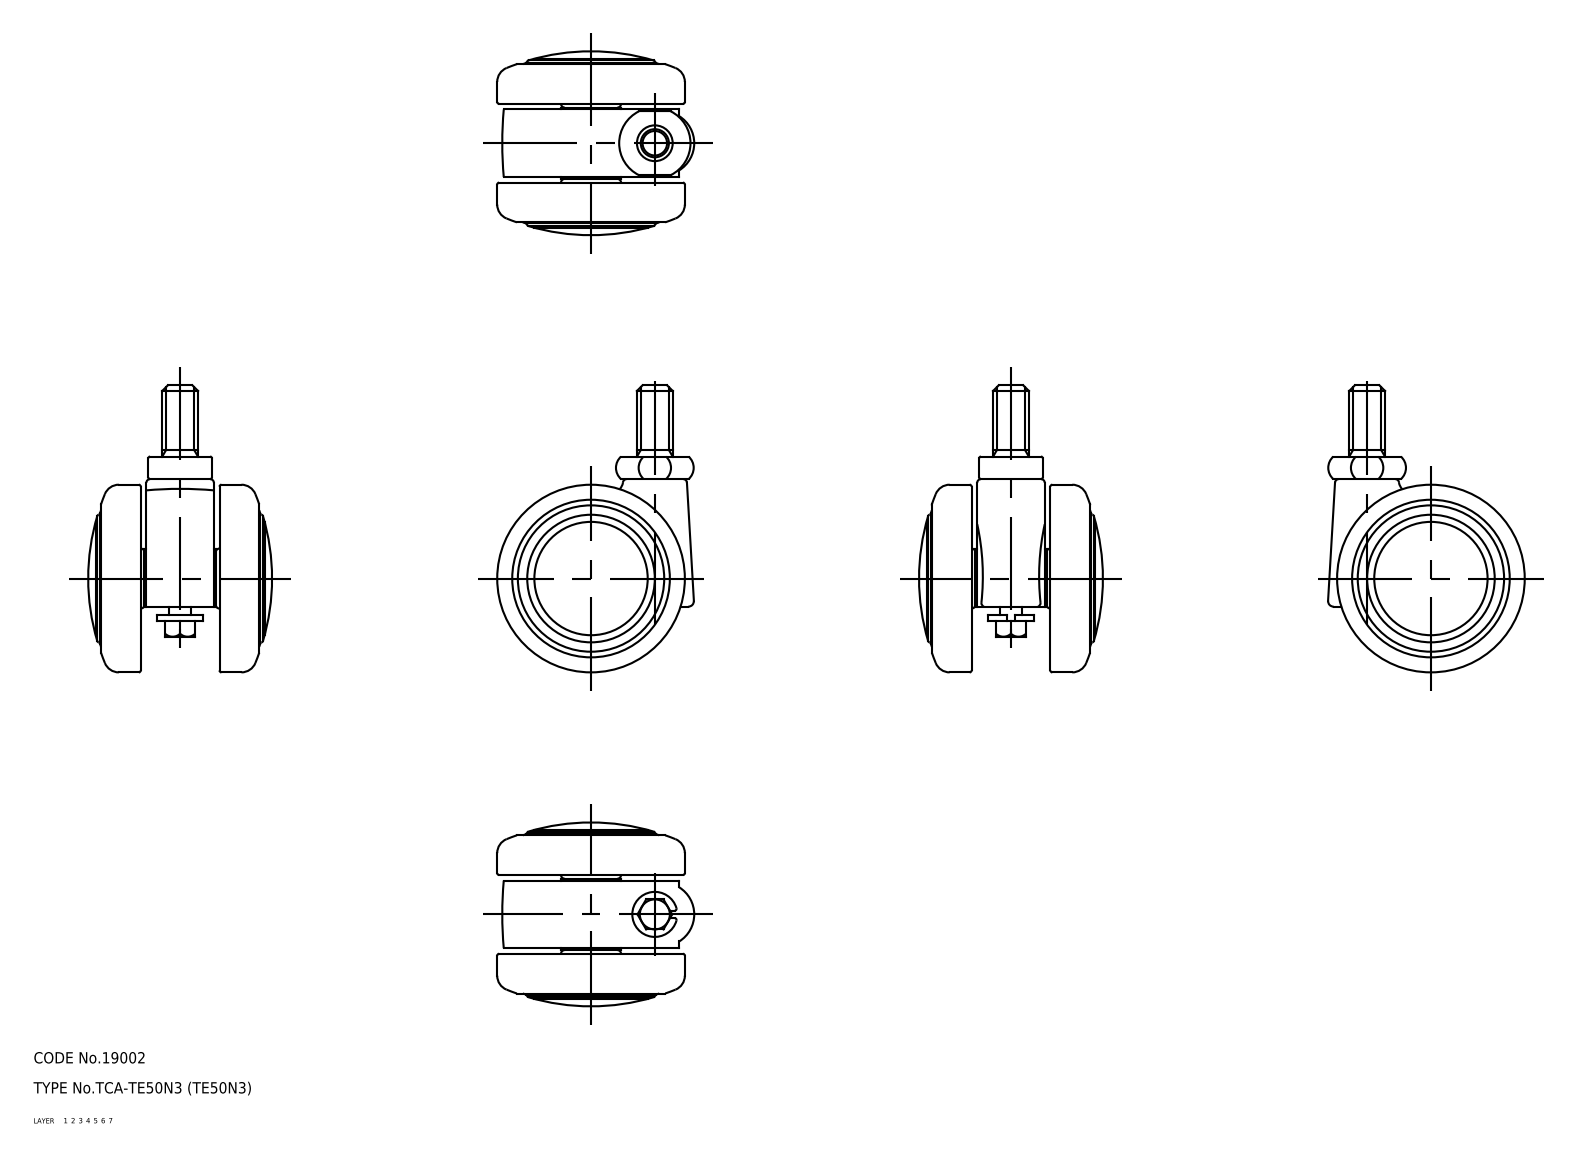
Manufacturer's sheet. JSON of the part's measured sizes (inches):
{"part_name": "wheel; main shaft; TE50N3_3383_36", "step_written_by": "CADfix (AUTOMOTIVE_DESIGN)", "units": "inches", "bodies": {"solids": 4, "faces": 136, "planar": 0, "cylindrical": 0, "other": 136}, "overall_size": [3.012, 2.064, 1.929], "volume_in3": 3.859, "surface_area_in2": 40.04}
